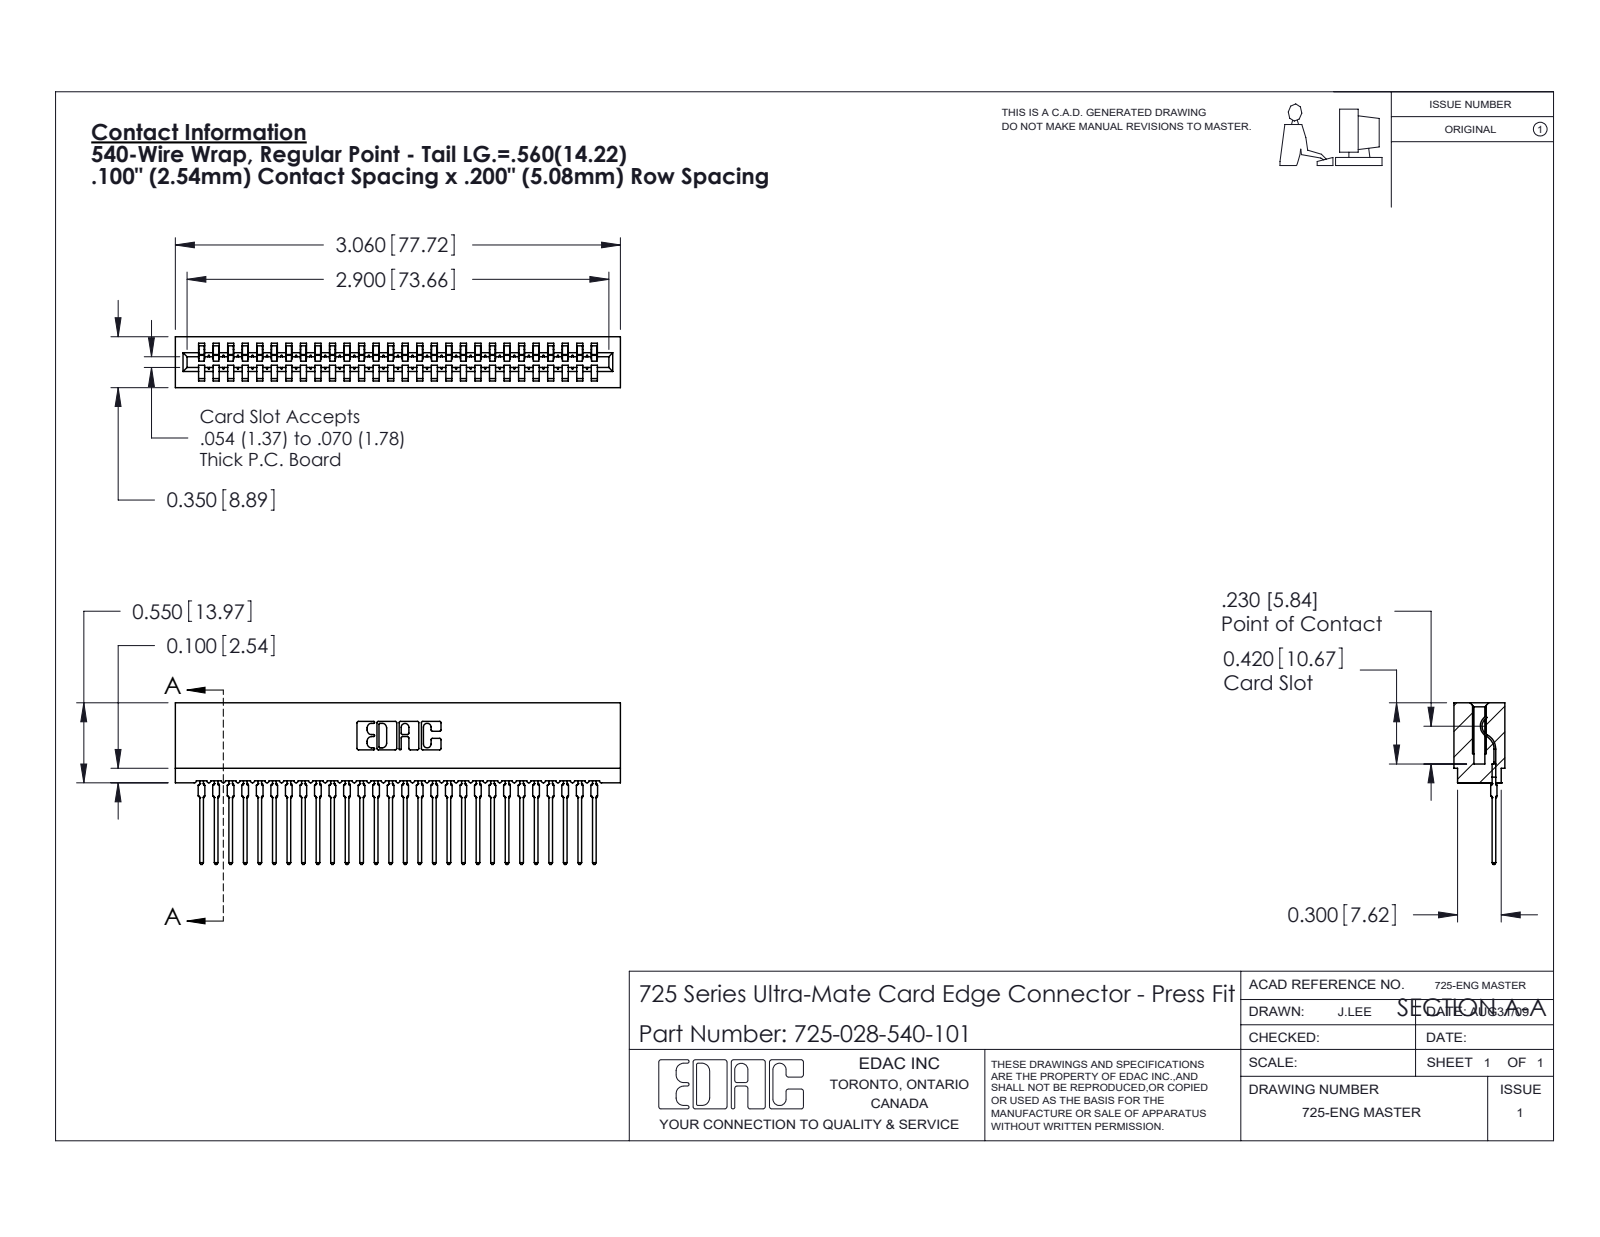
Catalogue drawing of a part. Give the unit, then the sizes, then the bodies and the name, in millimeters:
Units: millimetres
Overall size (bounding box): 77.7 × 28.2 × 8.9
Partial cylindrical surfaces — rounded edges, fillets, slot ends (radius × count): R0.4 ×56, R0.5 ×56, R0.3 ×22, R0.2 ×6, R0.8 ×6, R0.1 ×4, R0.3 ×4, R0.7 ×3
Main face-to-face distances: 5.1, 2.5, 8.9, 7.6, 12.7, 10.2, 5.4, 3.5, 15.2, 1.6
Volume: 6 050 mm³ · Surface area: 11 680 mm²
Bodies: 29 solids, 3231 faces (1931 planar, 572 cylindrical, 728 other)
Part name (STEP PRODUCT): 725 Part_Insulator Option - 01; 725-028-540-101; 745-292-001_540
STEP written by: SolidWorks 2020 (CONFIG_CONTROL_DESIGN)
